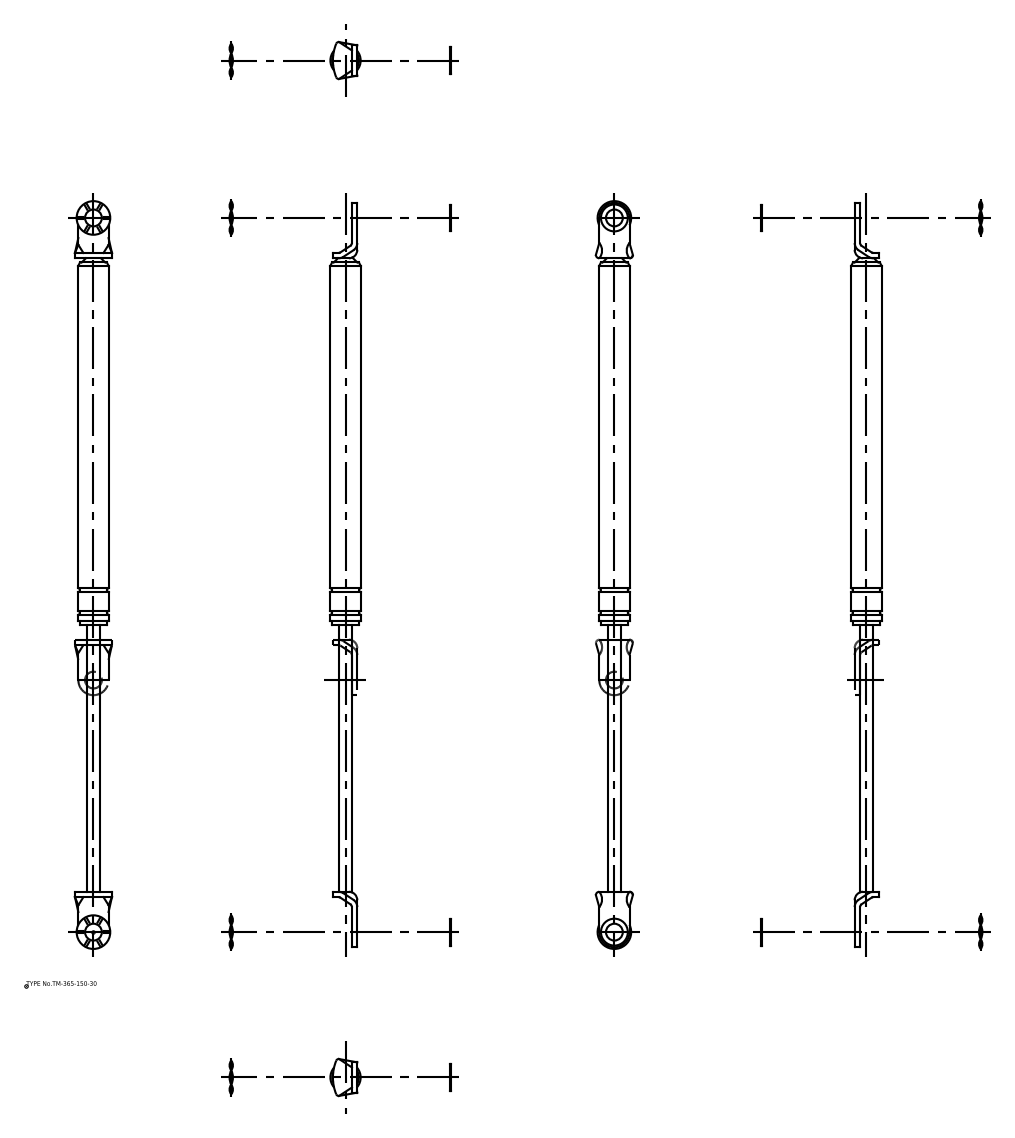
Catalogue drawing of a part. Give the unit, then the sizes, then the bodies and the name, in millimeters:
Units: millimetres
Overall size (bounding box): 445 × 22 × 18.5
Round holes (diameter × count): ⌀10 ×2
Round bosses / shafts (diameter × count): ⌀16 ×3, ⌀20 ×2, ⌀18.5 ×1, ⌀18 ×1, ⌀8 ×1
Partial cylindrical surfaces — rounded edges, fillets, slot ends (radius × count): R4.4 ×2, R5 ×2, R9 ×2, R26.32 ×1
Main face-to-face distances: 3.2, 2, 5.2, 380.2, 3.7, 5.7, 0.5, 221.2, 162.2, 383.4
Hole centre spacings: 425
Volume: 68 446 mm³ · Surface area: 22 337 mm²
Bodies: 6 solids, 94 faces (42 planar, 44 cylindrical, 8 other)
Part name (STEP PRODUCT): ウェーブワッシャー; ワッシャー; 本体; 本体_div
STEP written by: spGate 16.7.1 (AUTOMOTIVE_DESIGN)
